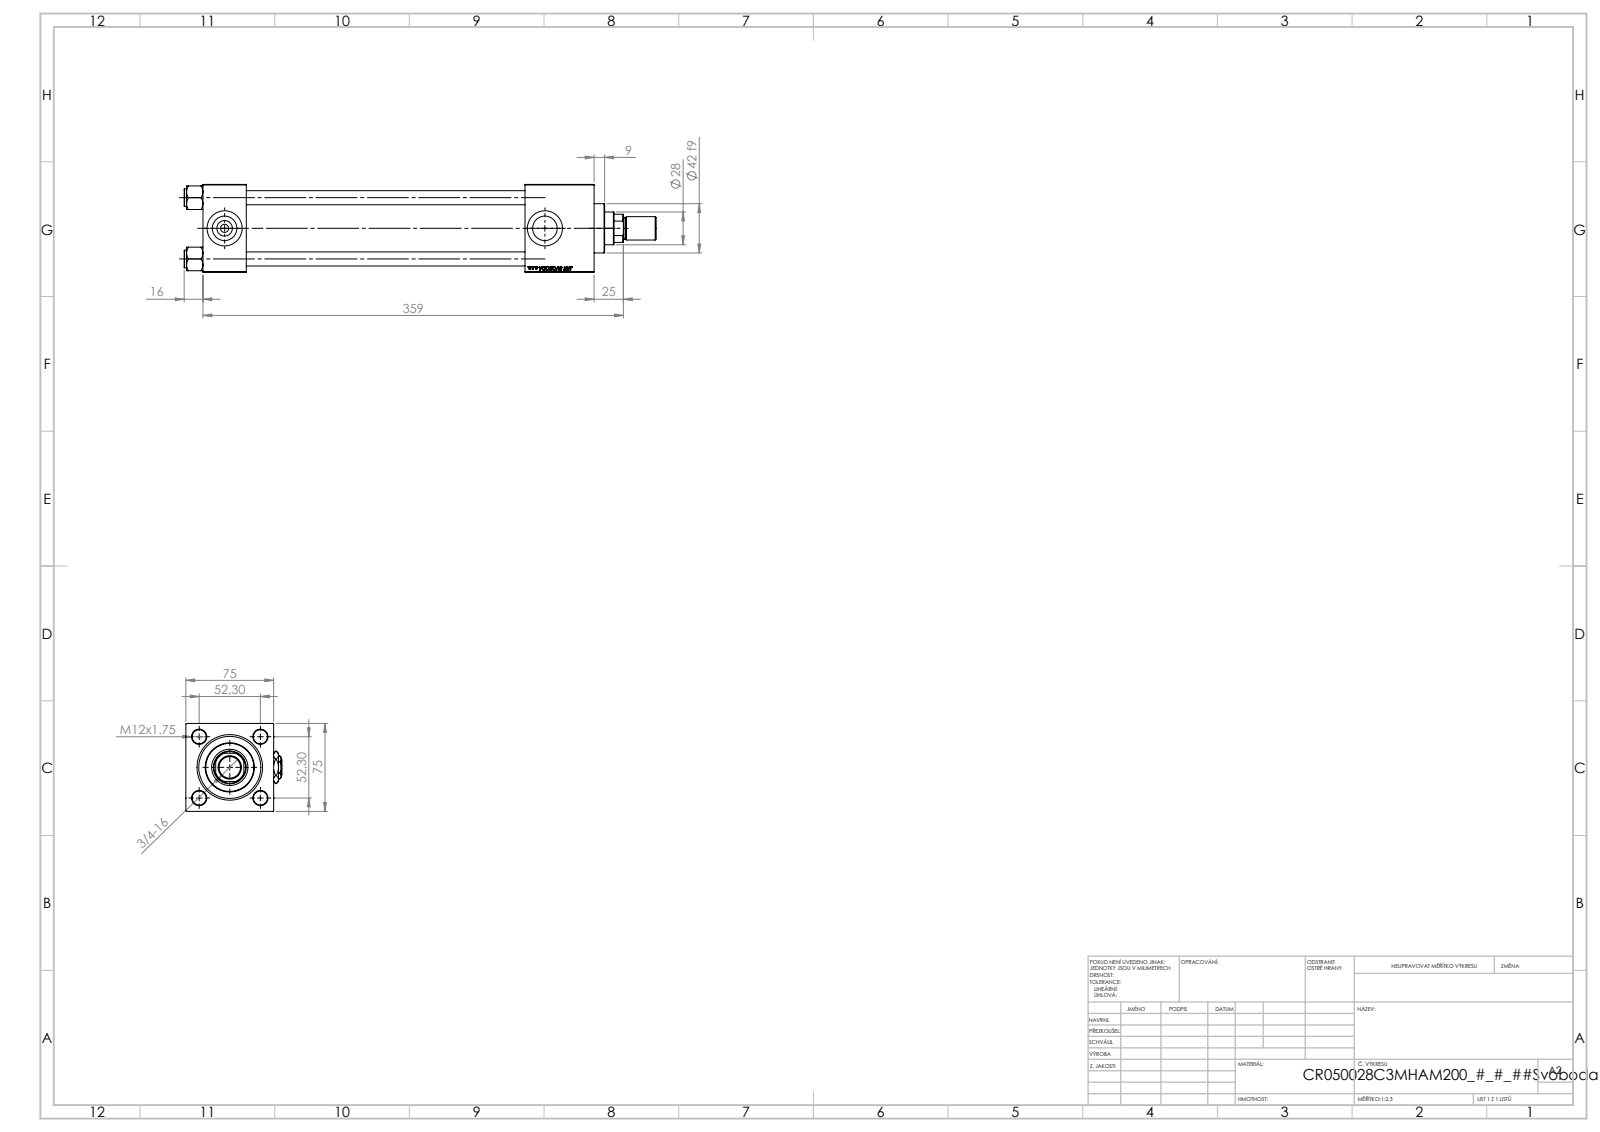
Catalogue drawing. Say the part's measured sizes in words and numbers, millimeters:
The part is named "V215CR_C_Body; Zatka_pro_OIL_PORT; ROD_END_AH; V215CR_VCP_C (+3 more)". Its 3-D file was written by "SolidWorks 2019 (CONFIG_CONTROL_DESIGN)". It is 14 solids with 1263 faces: 577 planar, 102 cylindrical and 584 other. Overall it measures 403 by 82.27 by 75 millimeters. Its volume is 954 790 cubic millimeters and its surface area 260 761 square millimeters. Round holes: 4 of diameter 12, 2 of diameter 7, 2 of diameter 20.96, 2 of diameter 30, 1 of diameter 18.5, 1 of diameter 28, 1 of diameter 31, 1 of diameter 41, 1 of diameter 50, 1 of diameter 53. Round bosses or shafts: 4 of diameter 15, 1 of diameter 56, 1 of diameter 42, 1 of diameter 20, 1 of diameter 18. Partial cylindrical surfaces (rounded edges, fillets, slot ends): 1 of radius 13.5. The main face-to-face distances are 75, 37, 334, 297, 275, 238, 59, 305.3, 268.3, 30.3. The hole center spacings are 36.98, 52.3, 73.96, 273.5.
